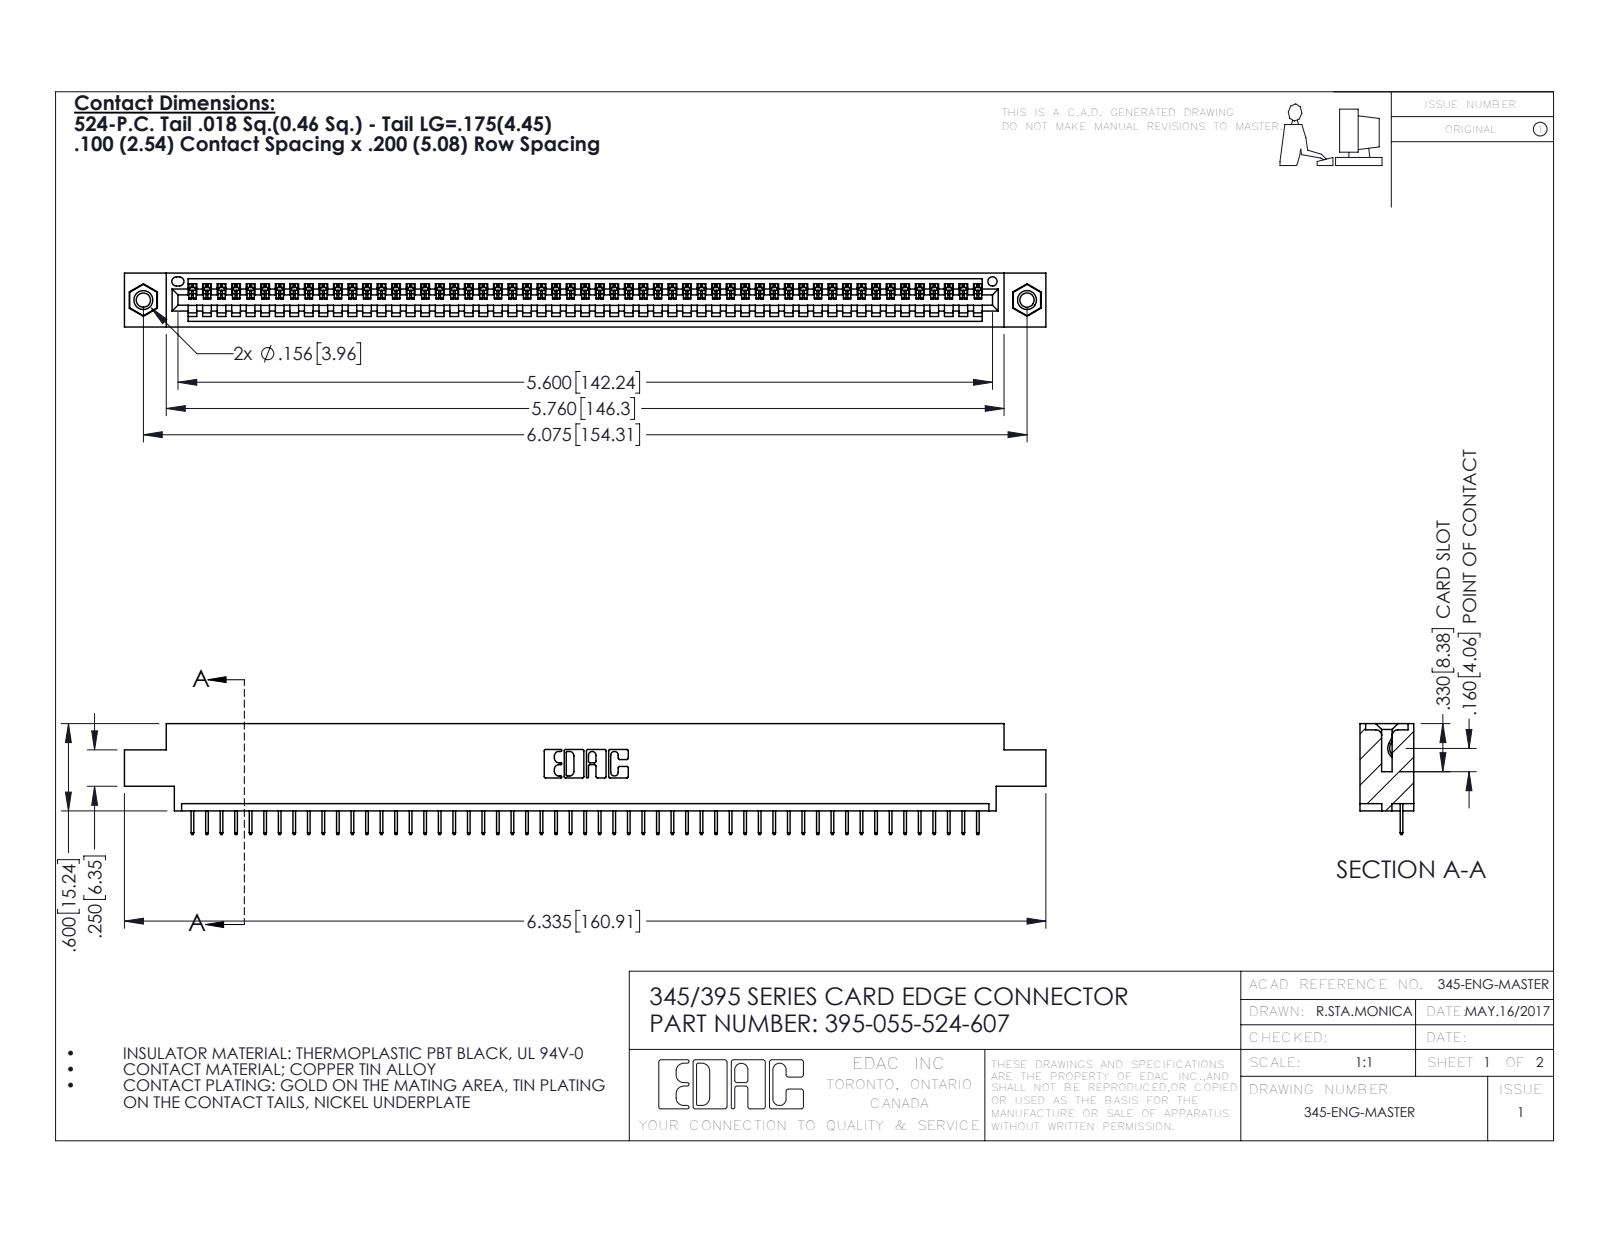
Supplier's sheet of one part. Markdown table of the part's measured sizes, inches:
| quantity | value |
| --- | --- |
| part name | 395-055-524-607; 345-292-001_345-293-124; 345-250-001_345-250-005-103; 345 Part_0.170 Offset - 0.156 Dia-TI |
| STEP written by | SolidWorks 2016 (CONFIG_CONTROL_DESIGN) |
| units | inches |
| bodies | 58 solids, 3600 faces (2646 planar, 938 cylindrical, 16 other) |
| overall size | 6.335 × 0.762 × 0.37 |
| volume | 0.918 in³ |
| surface area | 30.43 in² |
| round holes (diameter × count) | 0.098 × 2, 0.125 × 2, 0.156 × 2, 0.064 × 1 |
| round bosses / shafts (diameter × count) | 0.155 × 2 |
| partial cylindrical surfaces (radius × count) | 0.006 × 110, 0.01 × 22, 0.007 × 6, 0.031 × 6, 0.026 × 3, 0.031 × 2, 0.04 × 2, 0.014 × 1 |
| main face-to-face distances | 0.072, 0.298, 0.37, 0.2, 0.098, 0.272, 0.025, 0.225, 0.072, 0.175 |
| hole center spacings | 0.27, 5.839, 6.075 |
